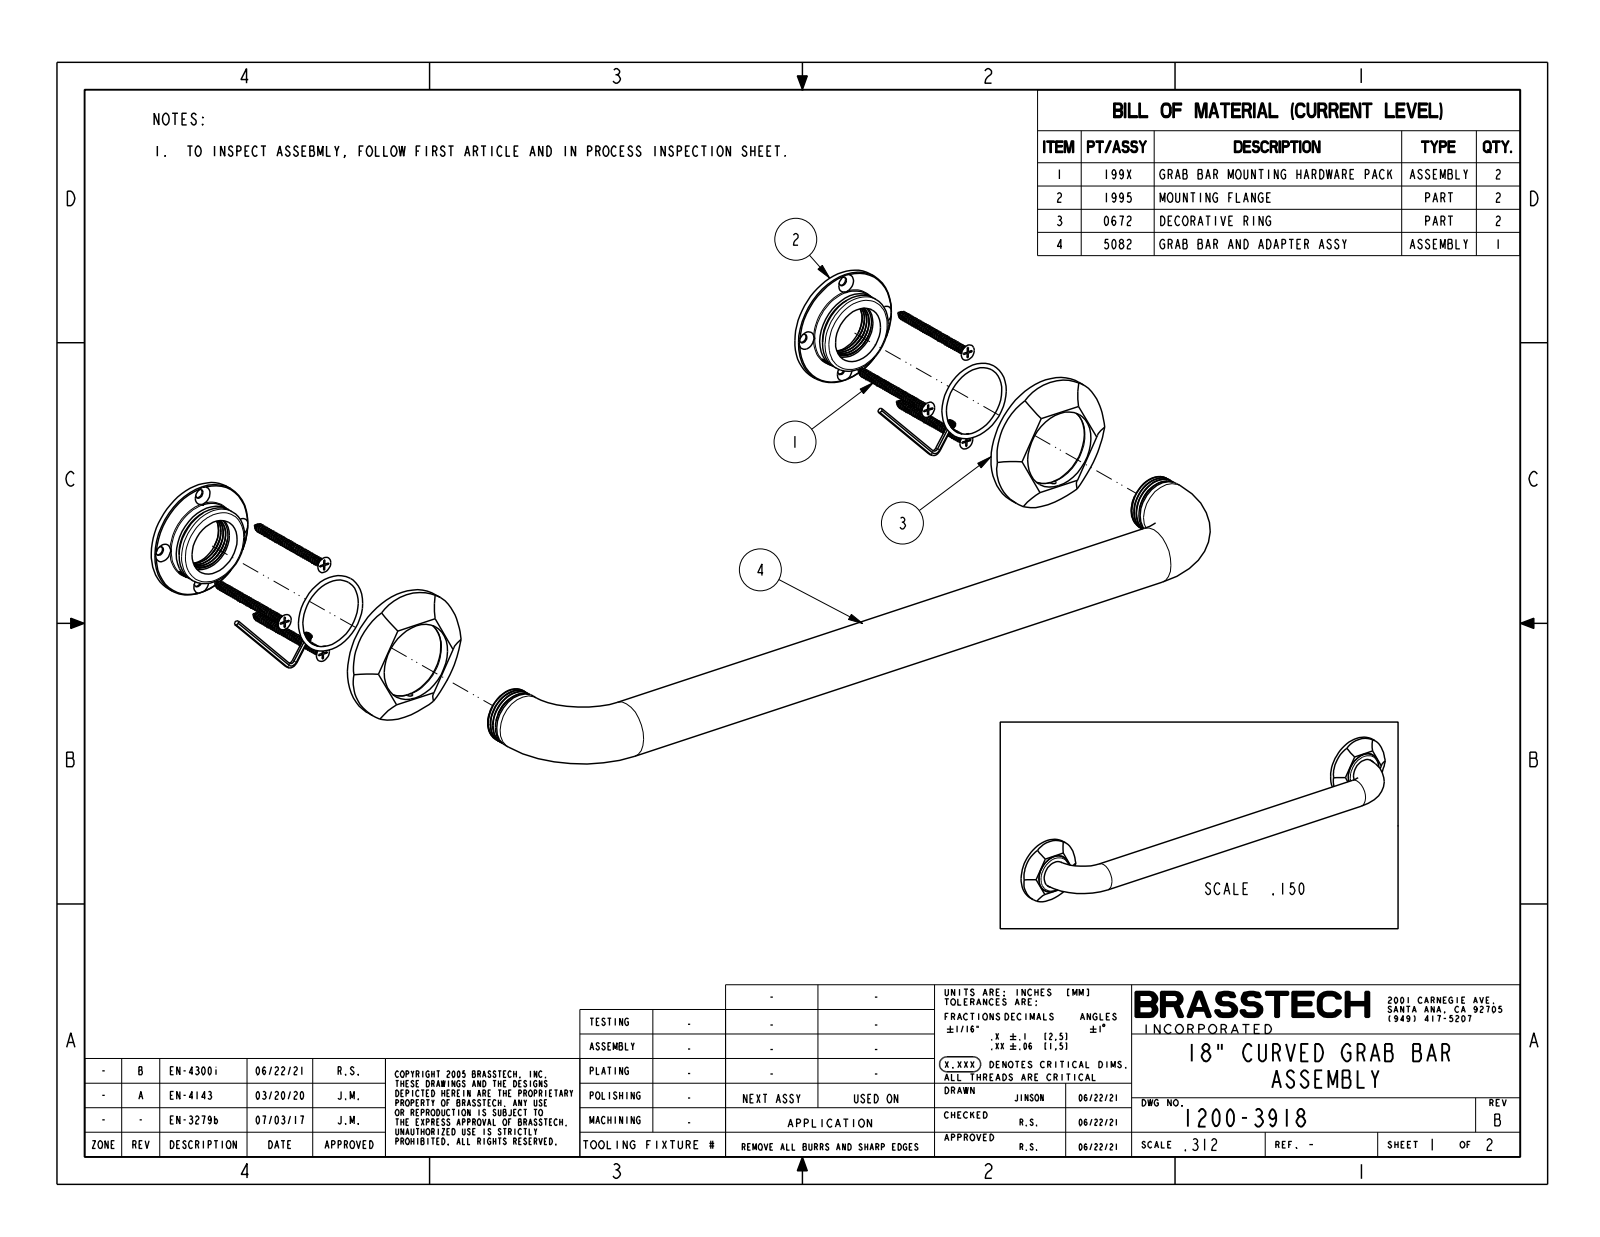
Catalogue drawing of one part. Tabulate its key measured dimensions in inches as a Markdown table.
| quantity | value |
| --- | --- |
| part name | 1200-3918_SW0001 |
| STEP written by | CREO PARAMETRIC BY PTC INC, 2018400 (CONFIG_CONTROL_DESIGN) |
| units | inches |
| bodies | 1 solid, 36 faces (6 planar, 22 cylindrical, 8 other) |
| overall size | 21 × 3 × 2.75 |
| volume | 30.02 in³ |
| surface area | 108.6 in² |
| round bosses / shafts (diameter × count) | 3 × 2, 1.75 × 2, 1.25 × 1 |
| partial cylindrical surfaces (radius × count) | 1.181 × 10 |
| main face-to-face distances | 0.6, 0.525, 0.075 |
